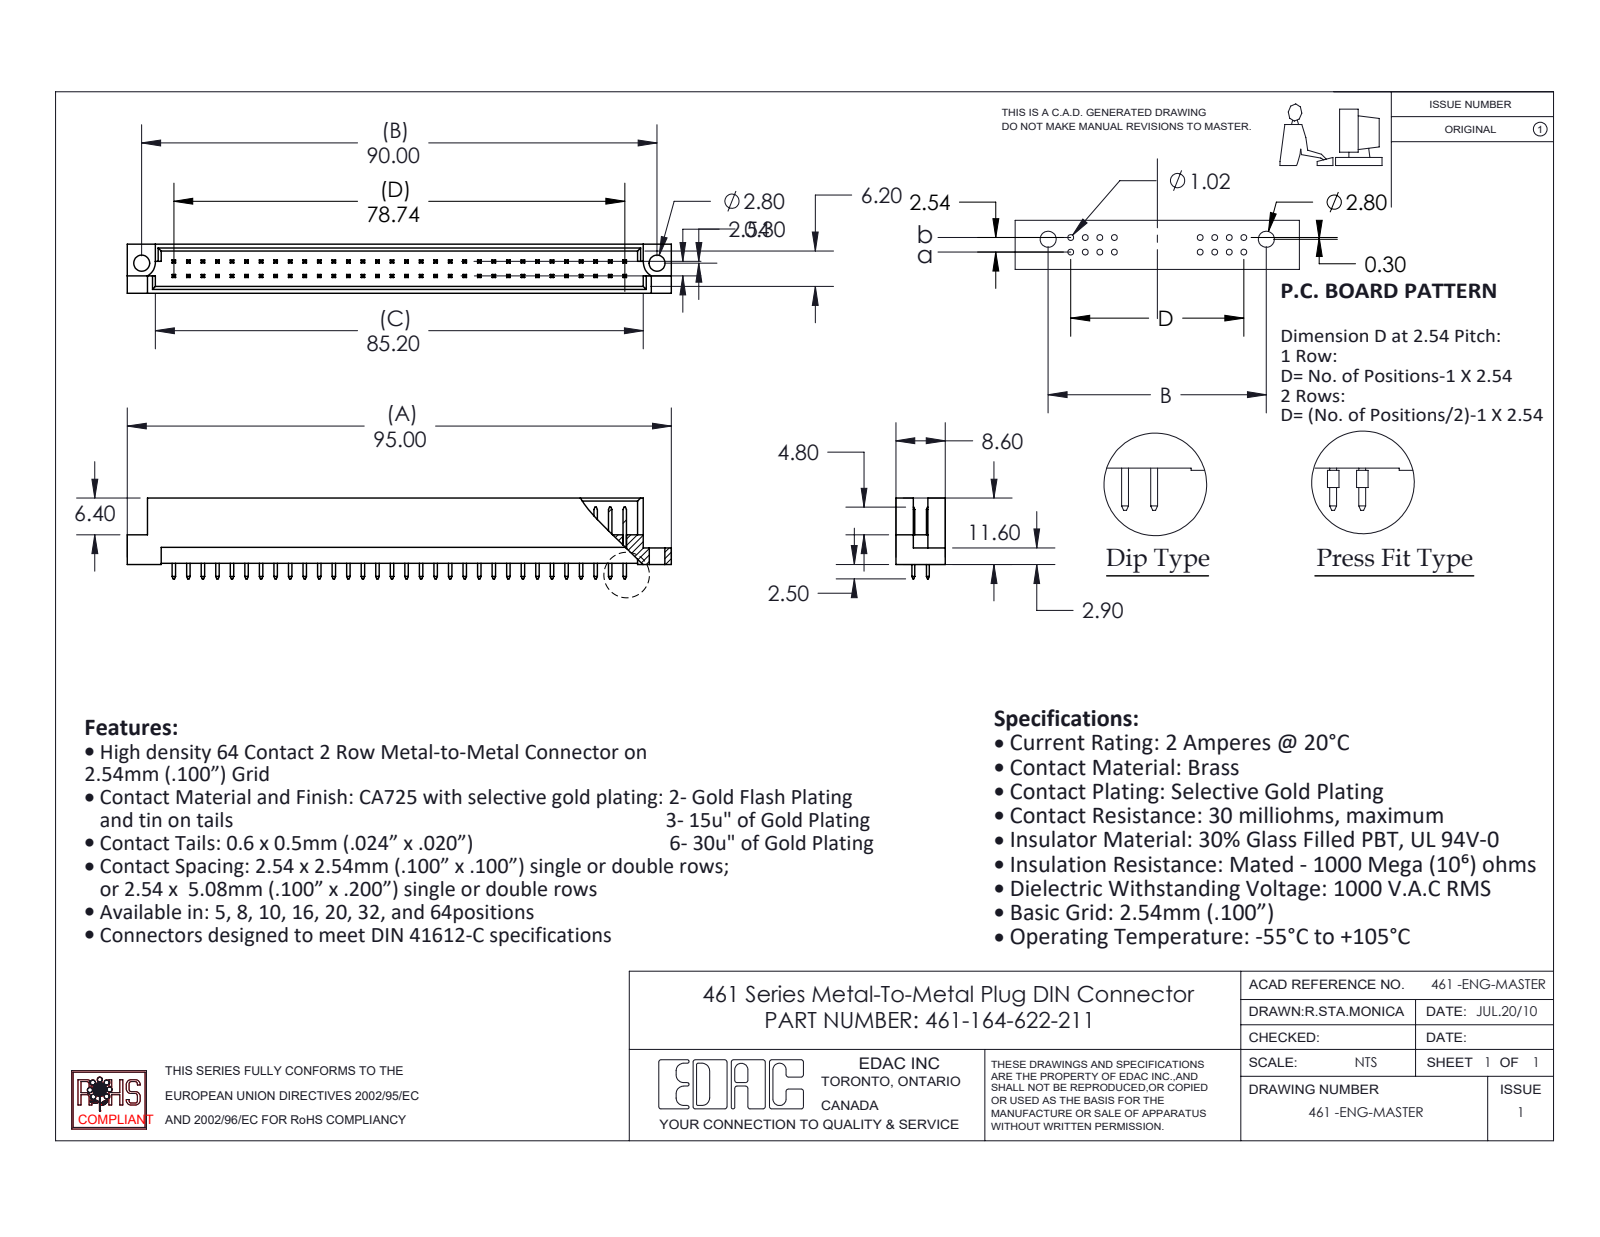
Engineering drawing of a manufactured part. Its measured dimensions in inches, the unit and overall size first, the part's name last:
Units: inches
Overall size (bounding box): 3.74 × 0.555 × 0.339
Round holes (diameter × count): ⌀0.11 ×2
Partial cylindrical surfaces — rounded edges, fillets, slot ends (radius × count): R0.11 ×2
Main face-to-face distances: 0.047, 0.291, 0.339, 0.1, 0.244, 0.129, 0.209, 0.082, 0.162, 0.109
Hole centre spacings: 3.543
Volume: 0.298 in³ · Surface area: 11.48 in²
Bodies: 65 solids, 1201 faces (1194 planar, 7 cylindrical, 0 other)
Part name (STEP PRODUCT): 461-290_22; 461-164-622-211; 461 Part_64
STEP written by: SolidWorks 2020 (CONFIG_CONTROL_DESIGN)
